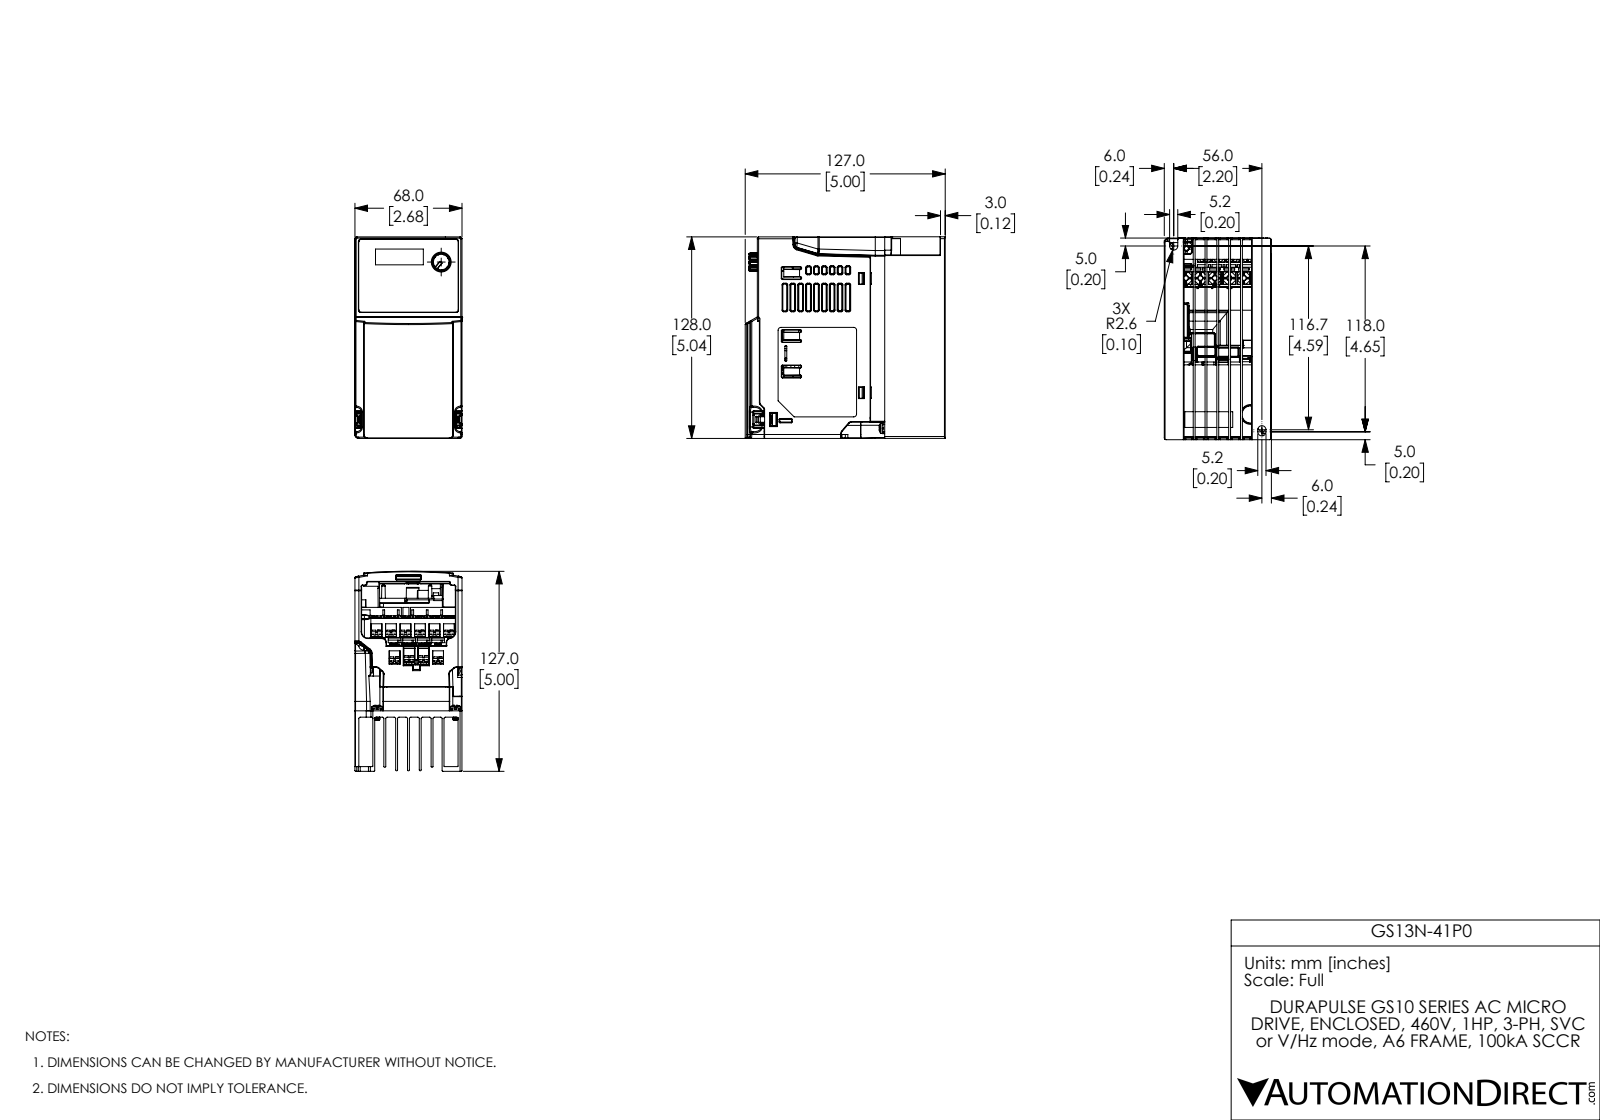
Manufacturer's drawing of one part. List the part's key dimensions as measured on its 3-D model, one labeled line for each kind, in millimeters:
Part name (STEP PRODUCT): DELTA_IA_MDS_VFD-ME300-A3_D-3D_20190924 from Step R1 red1 r3cC for A6bB
STEP written by: SolidWorks 2017 (AUTOMOTIVE_DESIGN)
Units: millimetres
Bodies: 33 solids, 5890 faces (3115 planar, 1270 cylindrical, 1505 other)
Overall size (bounding box): 128.04 × 127 × 68.03
Volume: 139 301 mm³ · Surface area: 186 110 mm²
Round holes (diameter × count): ⌀3.15 ×10, ⌀4.8 ×2, ⌀3.9 ×1, ⌀10.9 ×1, ⌀12.6 ×1
Round bosses / shafts (diameter × count): ⌀6.8 ×12, ⌀2.76 ×12, ⌀3.5 ×10, ⌀4.2 ×2, ⌀3.4 ×2
Partial cylindrical surfaces — rounded edges, fillets, slot ends (radius × count): R0.5 ×152, R0.3 ×145, R0.4 ×85, R0.2 ×70, R1 ×33, R0.8 ×30, R3 ×24, R1.2 ×23
Main face-to-face distances: 7.5, 1.2, 15, 29.5, 8.7, 6.3, 22, 14.5, 22.5, 37
Hole centre spacings: 9.2, 18.4, 14.34, 15.74, 18.23, 27.6, 21.43, 25.07
